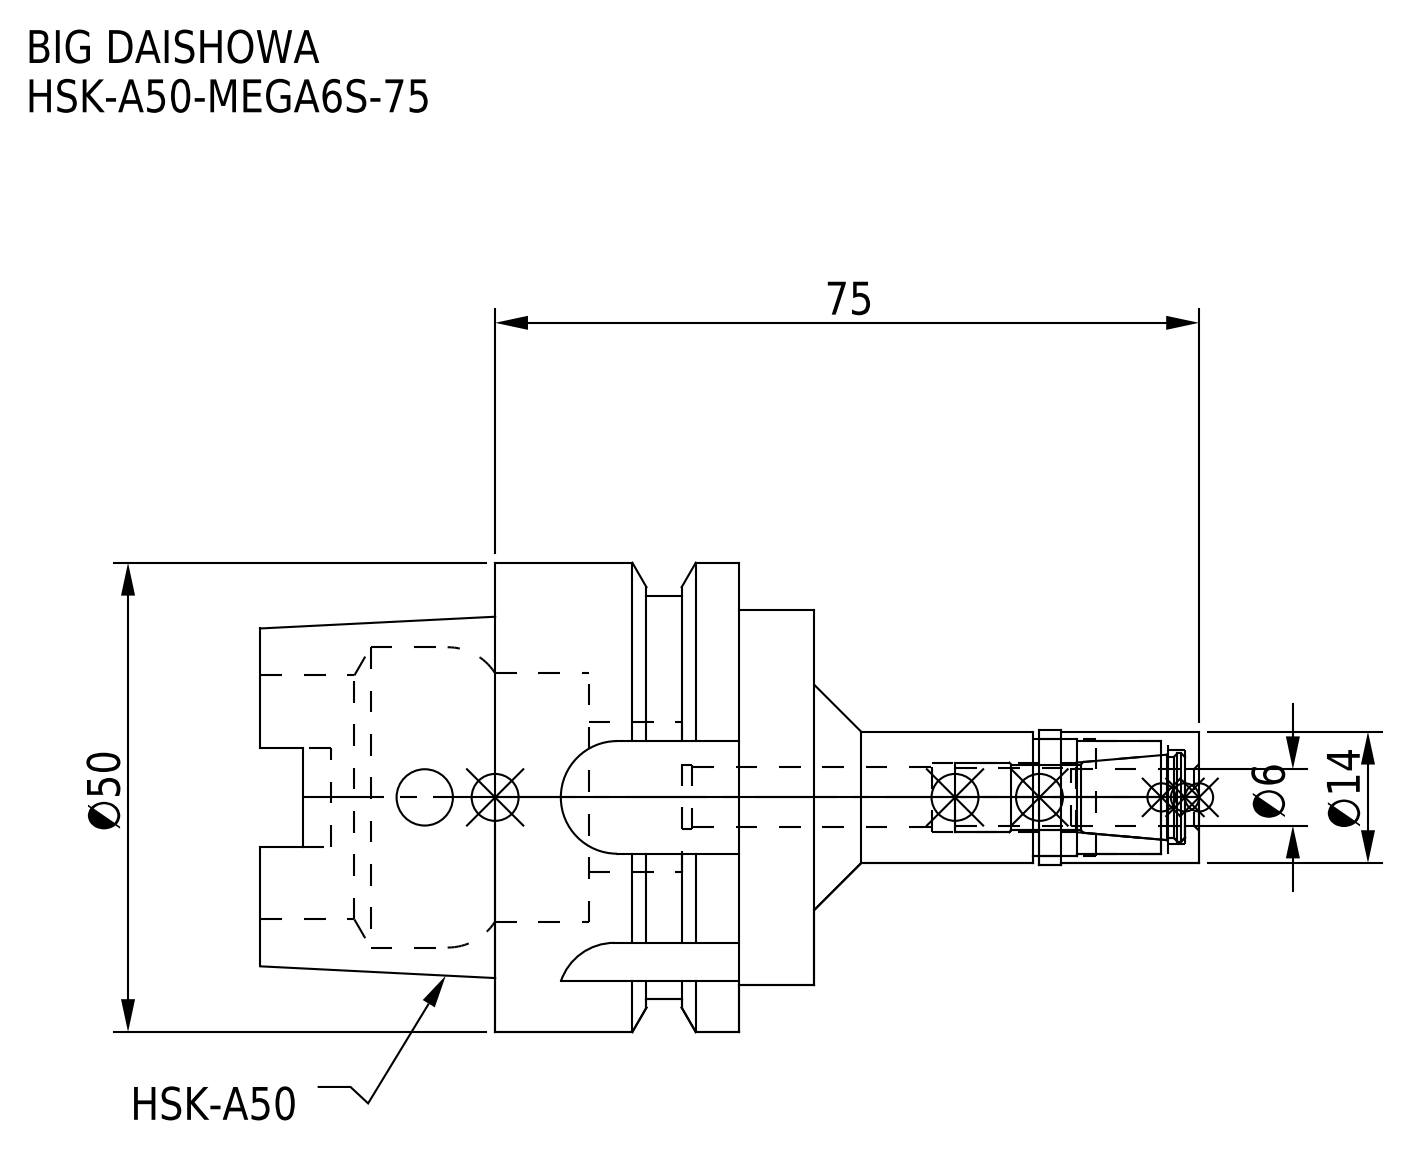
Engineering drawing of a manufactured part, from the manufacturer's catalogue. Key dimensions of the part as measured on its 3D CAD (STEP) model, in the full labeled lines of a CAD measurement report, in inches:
Part name (STEP PRODUCT): MGN6S_1.stp; HSK-A50-MEGA6S-75-060.stp; HSK-A50-MEGA6S-75_1.stp; HSK-A50-MEGA6S-75 (+3 more)
STEP written by: SolidWorks 2019 (CONFIG_CONTROL_DESIGN)
Units: inches
Bodies: 2 solids, 122 faces (47 planar, 55 cylindrical, 20 other)
Overall size (bounding box): 3.937 × 1.969 × 1.969
Volume: 3.904 in³ · Surface area: 31.32 in²
Round holes (diameter × count): ⌀0.236 ×1, ⌀0.24 ×1, ⌀0.252 ×1, ⌀0.268 ×1, ⌀0.291 ×1, ⌀0.394 ×1, ⌀0.472 ×1, ⌀0.492 ×1, ⌀0.63 ×1, ⌀1.024 ×1, ⌀1.047 ×1, ⌀1.26 ×1
Round bosses / shafts (diameter × count): ⌀1.969 ×1, ⌀1.693 ×1, ⌀1.575 ×1, ⌀0.563 ×1, ⌀0.551 ×1
Partial cylindrical surfaces — rounded edges, fillets, slot ends (radius × count): R0.094 ×4, R0.236 ×4
Main face-to-face distances: 1.339, 0.315, 1.024, 0.947, 0.632, 0.392, 2.008, 2.323, 1.376, 0.984
